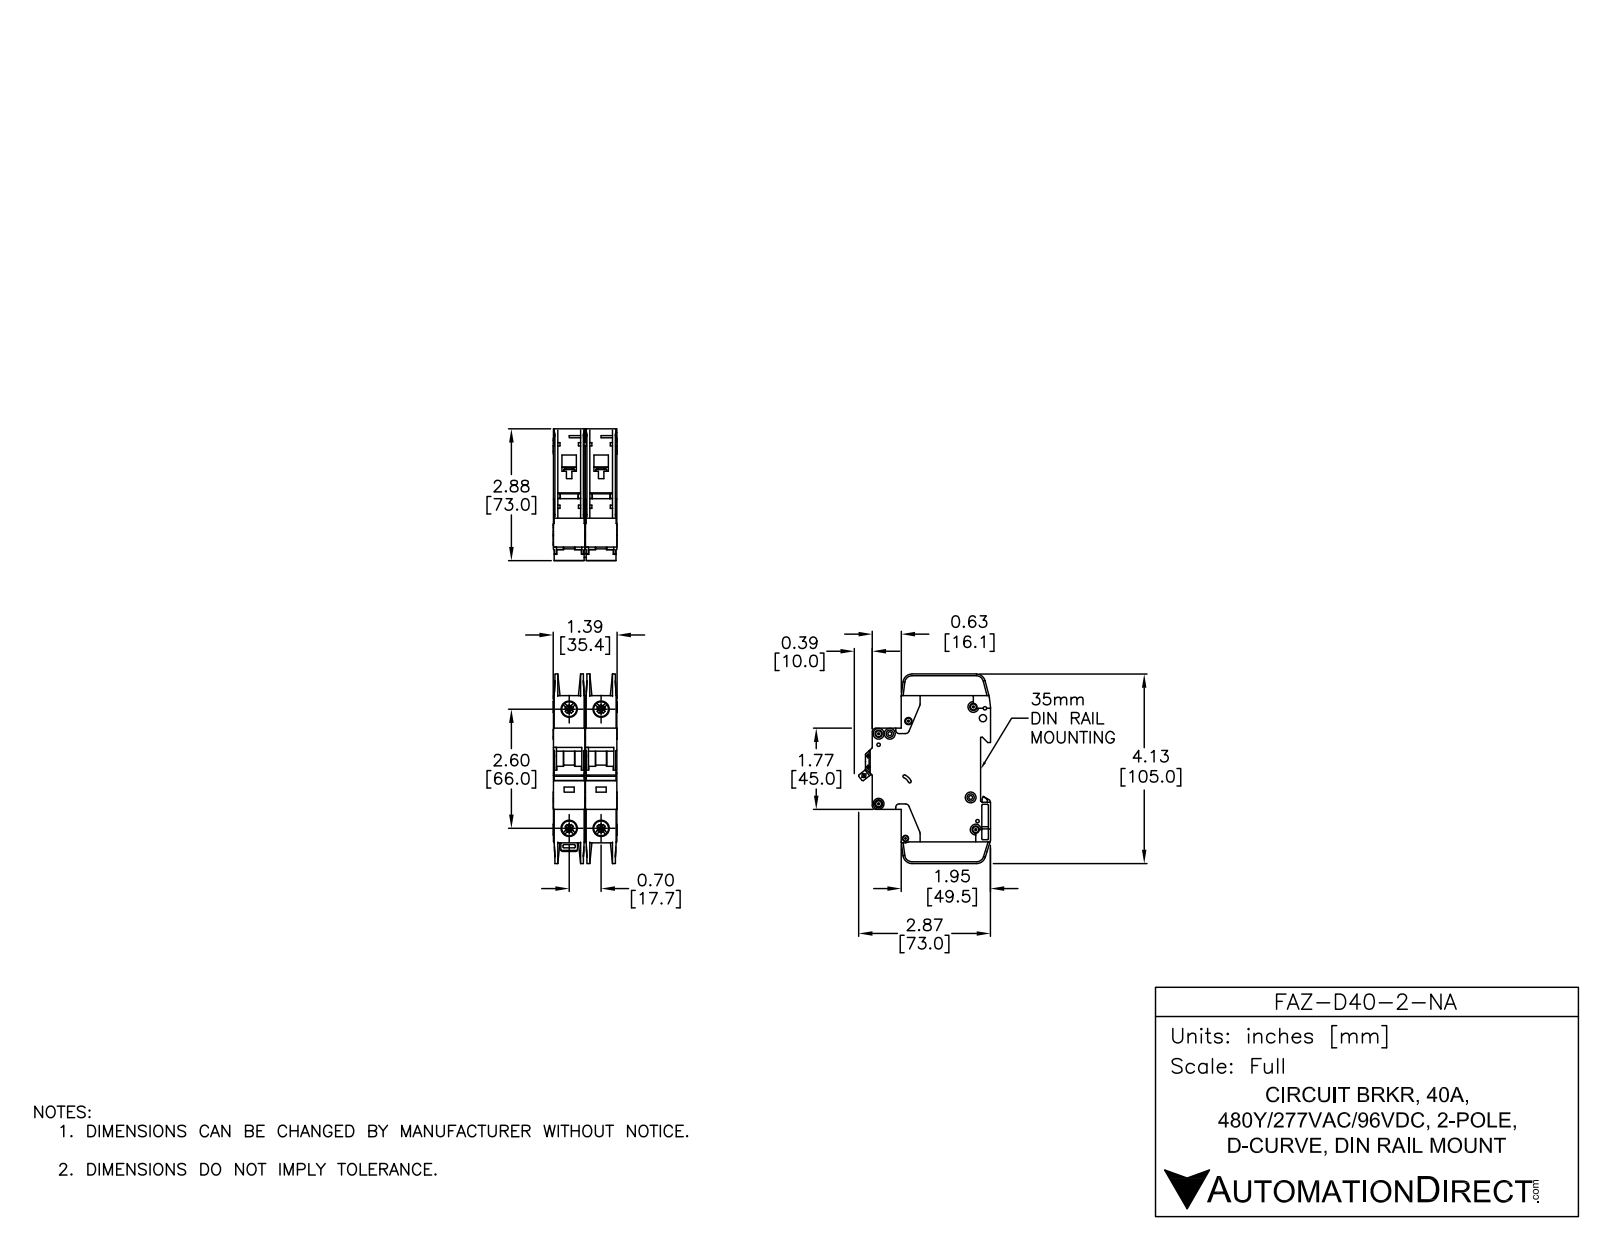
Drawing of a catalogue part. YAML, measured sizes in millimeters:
part_name: "FAZ-D40-2-NA"
step_written_by: "SolidWorks 2014 (AUTOMOTIVE_DESIGN)"
units: millimeters
bodies: {solids: 6, faces: 1568, planar: 818, cylindrical: 526, other: 224}
overall_size: [105, 73.04, 35.4]
volume: 155390
surface_area: 49479
round_holes:
  - {diameter: 3.6, count: 7}
  - {diameter: 7.15, count: 4}
  - {diameter: 8.2, count: 4}
  - {diameter: 1.09, count: 2}
  - {diameter: 1.5, count: 2}
  - {diameter: 4, count: 2}
  - {diameter: 1.9, count: 1}
  - {diameter: 2.15, count: 1}
  - {diameter: 2.2, count: 1}
  - {diameter: 2.55, count: 1}
  - {diameter: 3.3, count: 1}
  - {diameter: 3.4, count: 1}
round_bosses_or_shafts:
  - {diameter: 6, count: 7}
  - {diameter: 2.5, count: 2}
partial_cylinders:
  - {radius: 0.25, count: 47}
  - {radius: 0.5, count: 24}
  - {radius: 1, count: 18}
  - {radius: 2, count: 12}
  - {radius: 5, count: 5}
  - {radius: 1.8, count: 4}
  - {radius: 4, count: 4}
  - {radius: 0.2, count: 2}
face_to_face_distances: [17.7, 17.5, 0.7, 15.05, 2.45, 1.75, 15.75, 13.3, 35.2, 17]
hole_center_spacings: [6.2, 17.7, 66, 68.33, 5.19, 6.1, 8.19, 8.56]
